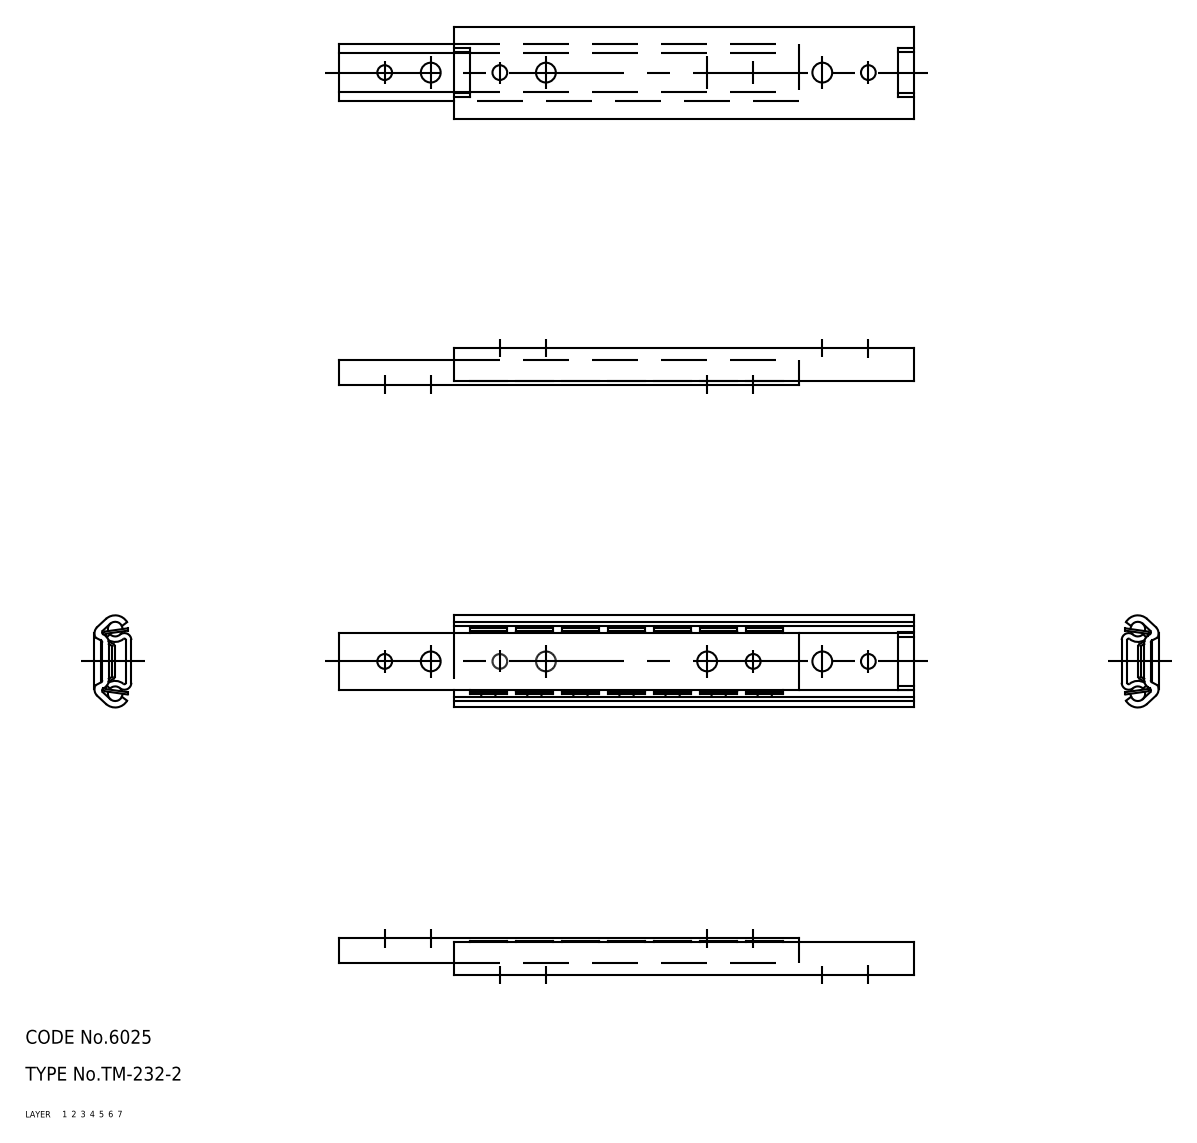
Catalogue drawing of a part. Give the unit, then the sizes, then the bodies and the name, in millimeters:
Units: millimetres
Overall size (bounding box): 125 × 20 × 8
Volume: 7 029 mm³ · Surface area: 13 719 mm²
Bodies: 17 solids, 244 faces (0 planar, 0 cylindrical, 244 other)
Part name (STEP PRODUCT): ball; retainer; member_B; member_A (+1 more)
STEP written by: CADfix (AUTOMOTIVE_DESIGN)
